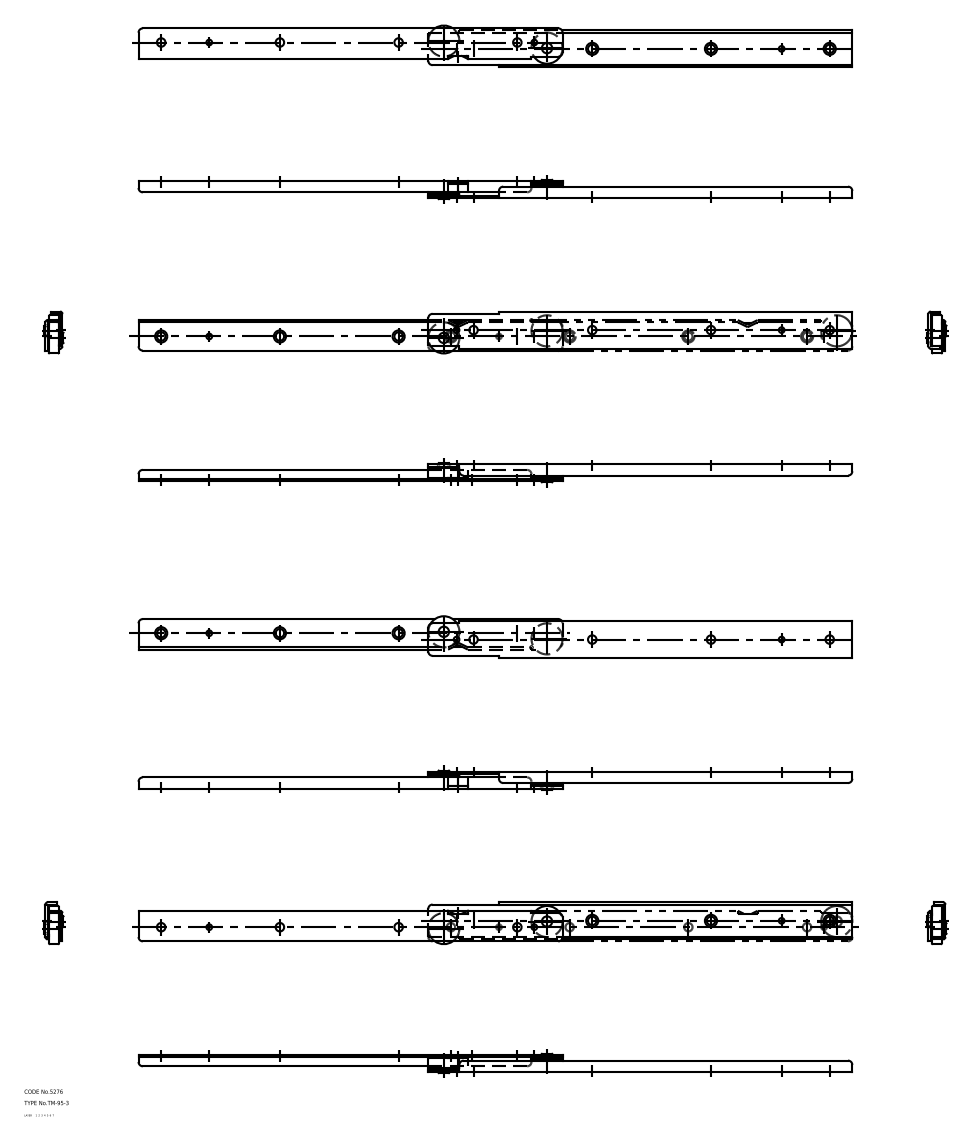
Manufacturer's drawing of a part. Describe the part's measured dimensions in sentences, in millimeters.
The part is named "roller; member_B; member_A; TM_95_3_7313_36". Its 3-D file was written by "CADfix (AUTOMOTIVE_DESIGN)". It is 4 solids with 117 faces: 0 planar, 0 cylindrical and 117 other. Overall it measures 505 by 29.6 by 13.4 millimeters. Its volume is 35 311 cubic millimeters and its surface area 42 435 square millimeters.
